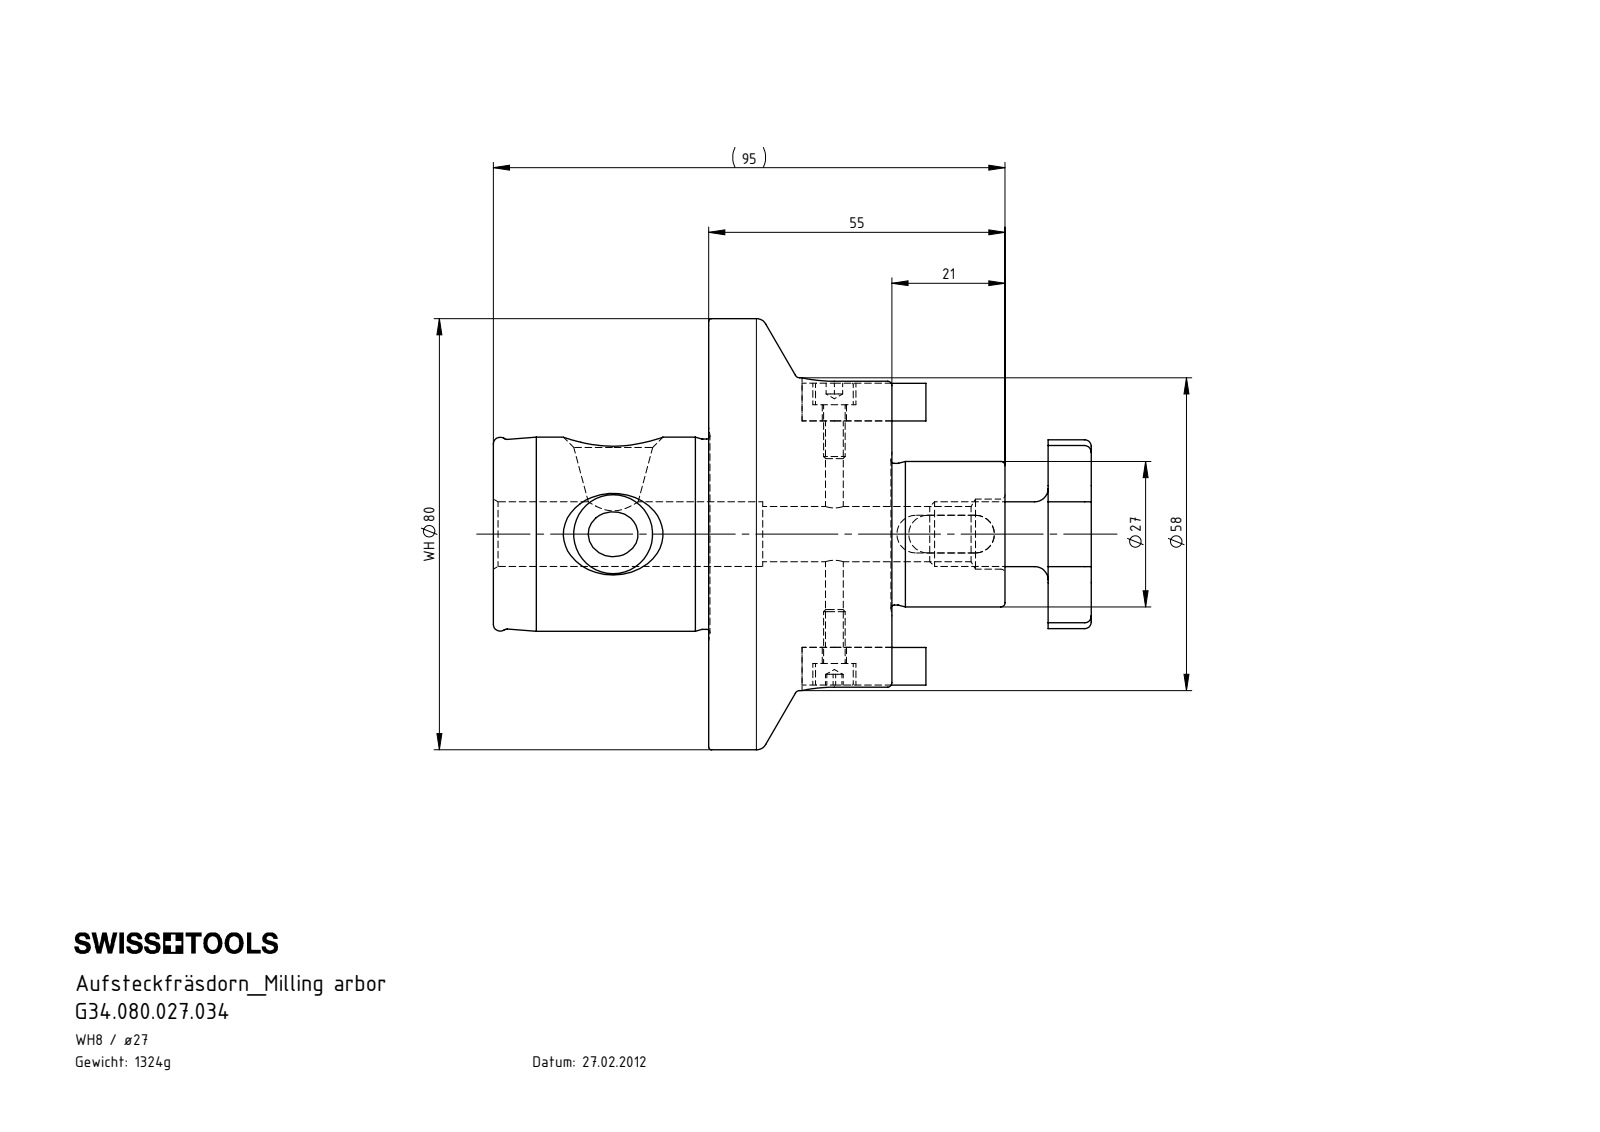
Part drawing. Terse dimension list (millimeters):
name: ISO 4762 - M4 x 10_PreviewCfg; WH8.D27.001.034; WH8-D27.001.034_A; D27-ER3.001.018_A (+2 more)
written by: SolidWorks 2022 (AUTOMOTIVE_DESIGN)
unit: mm
bodies: 7 solids, 210 faces (71 planar, 60 cylindrical, 79 other)
size: 111 × 80 × 80
volume: 169 157 mm³; area: 33 132 mm²
holes: 1× ⌀3.3, 1× ⌀4.5, 1× ⌀8, 1× ⌀10.25, 1× ⌀12, 1× ⌀13
bosses: 1× ⌀80, 1× ⌀58, 1× ⌀36, 1× ⌀35.3, 1× ⌀27, 1× ⌀26.3, 1× ⌀7, 1× ⌀4
rounds: 4× R3, 3× R3.5, 1× R6, 1× R17.5
face distances: 34, 8, 7, 40, 74, 12, 111, 71, 37, 49
